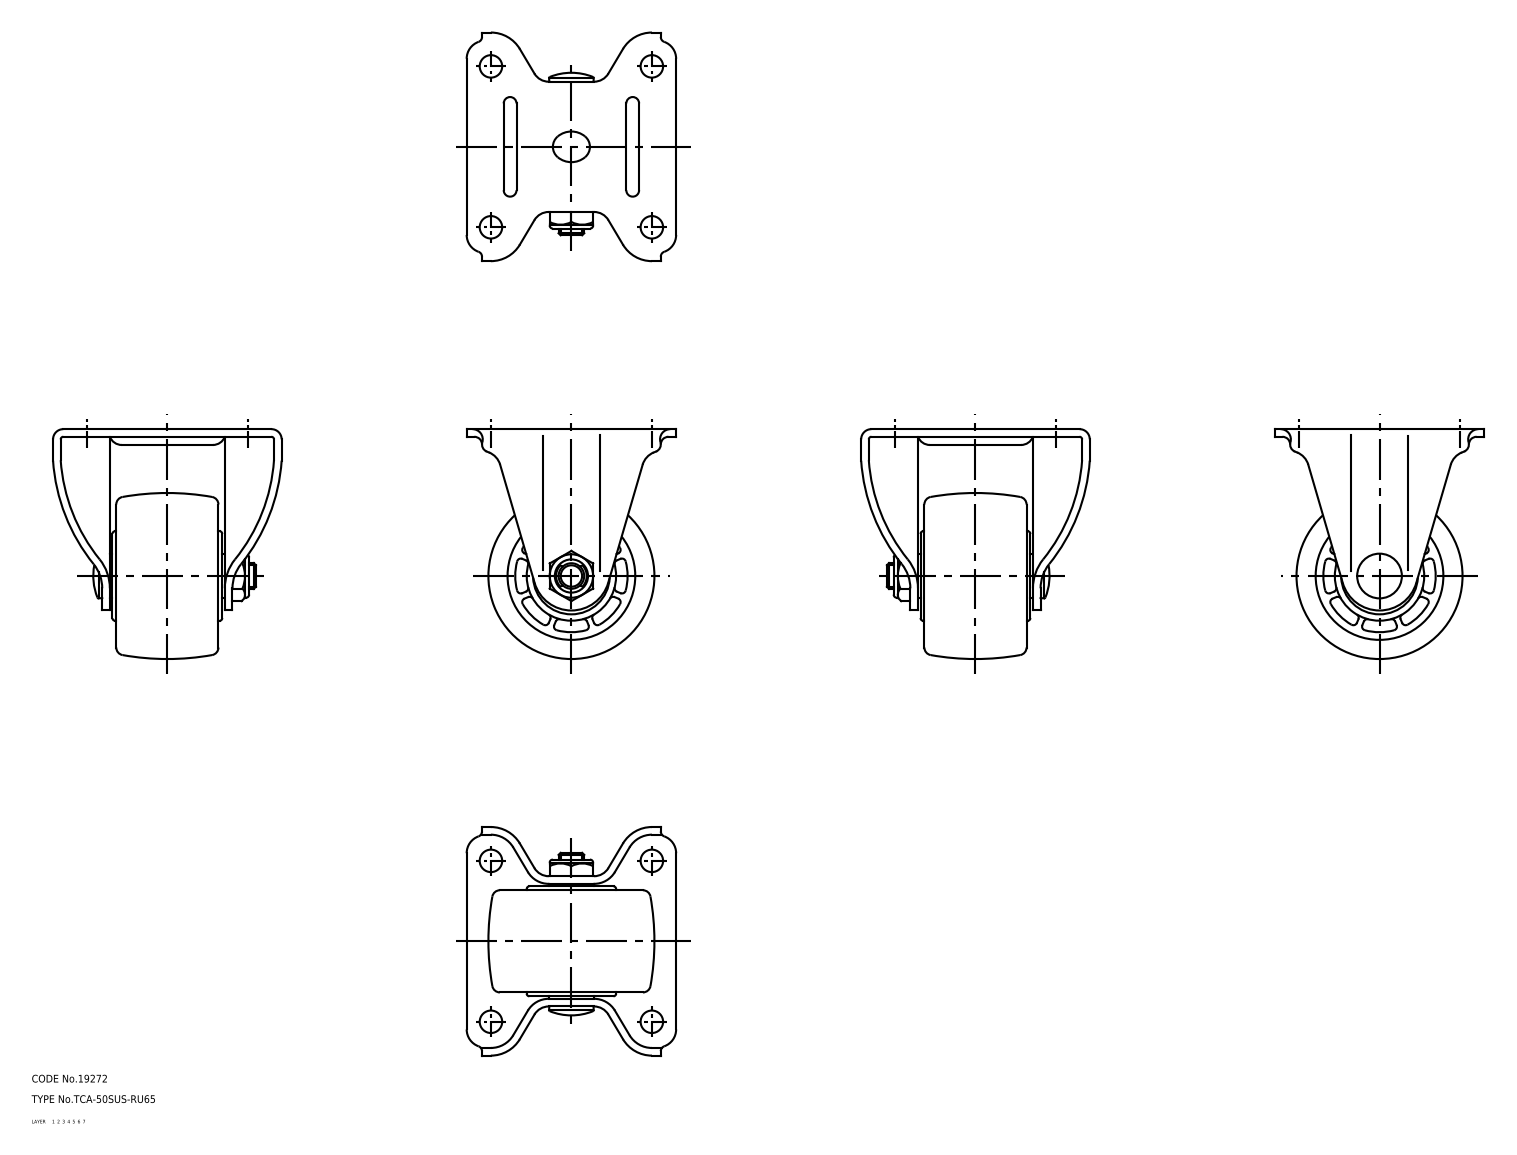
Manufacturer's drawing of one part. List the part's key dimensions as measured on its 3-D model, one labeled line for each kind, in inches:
Part name (STEP PRODUCT): 67126065; 67126078; 67126091; 67126104
STEP written by: CADfix (AUTOMOTIVE_DESIGN)
Units: inches
Bodies: 4 solids, 299 faces (0 planar, 0 cylindrical, 299 other)
Overall size (bounding box): 3.543 × 3.524 × 3.228
Volume: 9.333 in³ · Surface area: 87.51 in²
